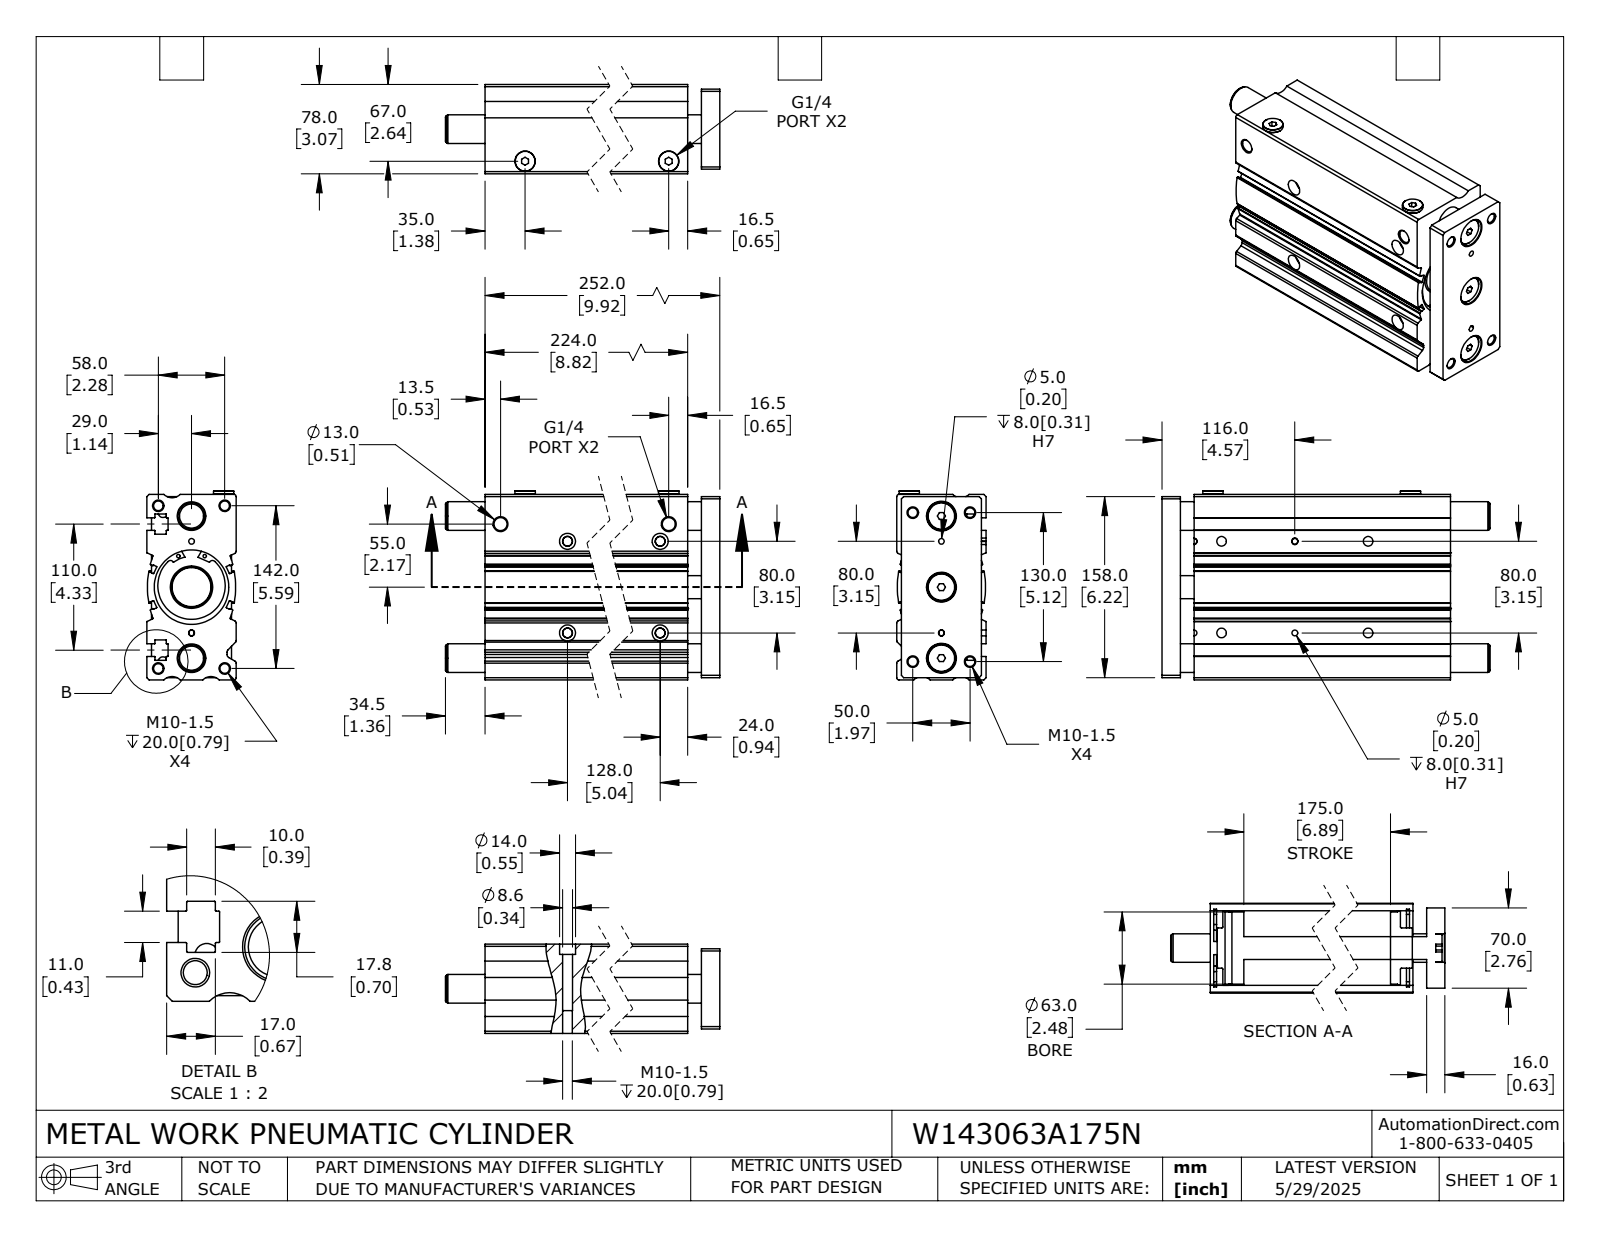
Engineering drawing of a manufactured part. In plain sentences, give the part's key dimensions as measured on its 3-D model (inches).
The part is named "W143063A175N_BODY; W143063A175N_ROD; W143063A175N". Its 3-D file was written by "SolidWorks 2024 (CONFIG_CONTROL_DESIGN)". It is 6 solids with 465 faces: 187 planar, 222 cylindrical and 56 other. Overall it measures 11.28 by 6.496 by 3.071 inches. Its volume is 134.8 cubic inches and its surface area 583.1 square inches. Round holes: 12 of diameter 0.33, 4 of diameter 0.118, 4 of diameter 0.197, 4 of diameter 0.339, 4 of diameter 0.551, 3 of diameter 0.984, 2 of diameter 0.448, 1 of diameter 2.559. Round bosses or shafts: 3 of diameter 0.945, 2 of diameter 0.697, 1 of diameter 2.677, 1 of diameter 2.551, 1 of diameter 2.48, 1 of diameter 1.378, 1 of diameter 0.787. Partial cylindrical surfaces (rounded edges, fillets, slot ends): 44 of radius 0.012, 12 of radius 0.02, 8 of radius 0.079, 8 of radius 0.098, 4 of radius 0.118, 3 of radius 0.394, 2 of radius 0.124, 2 of radius 1.157. The main face-to-face distances are 3.071, 6.378, 0.63, 4.331, 0.472, 1.102, 9.921, 9.291, 8.819, 0.134. The hole center spacings are 0.284, 0.682, 0.991, 1.158, 1.195, 1.392, 1.448, 1.585.
